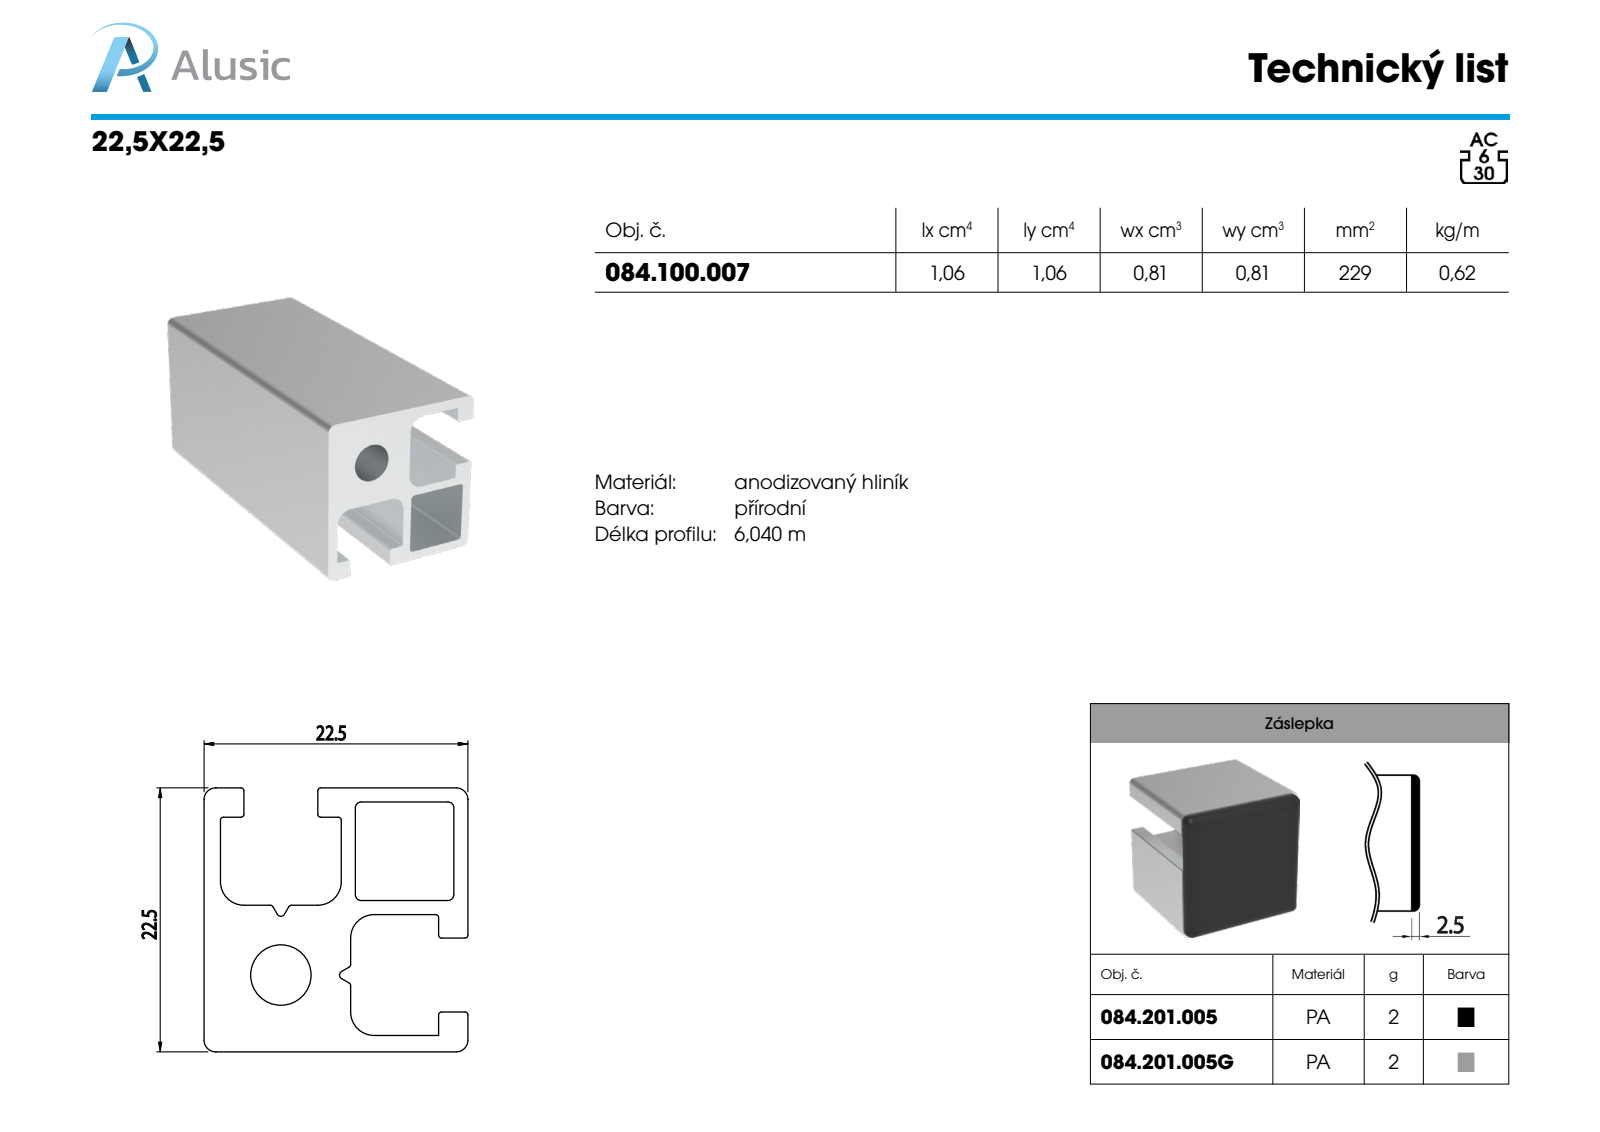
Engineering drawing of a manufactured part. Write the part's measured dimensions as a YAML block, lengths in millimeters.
part_name: "084.201.005"
step_written_by: "SolidWorks 2011 (CONFIG_CONTROL_DESIGN)"
units: millimeters
bodies: {solids: 1, faces: 34, planar: 10, cylindrical: 16, other: 8}
overall_size: [22, 22, 10.5]
volume: 1323
surface_area: 1568
round_holes:
  - {diameter: 4, count: 1}
  - {diameter: 6.2, count: 1}
round_bosses_or_shafts:
  - {diameter: 8, count: 1}
  - {diameter: 5, count: 1}
partial_cylinders:
  - {radius: 1, count: 4}
  - {radius: 2, count: 4}
face_to_face_distances: [2.5, 22, 10.5, 8, 4, 6.5]
hole_center_spacings: [14.5]
